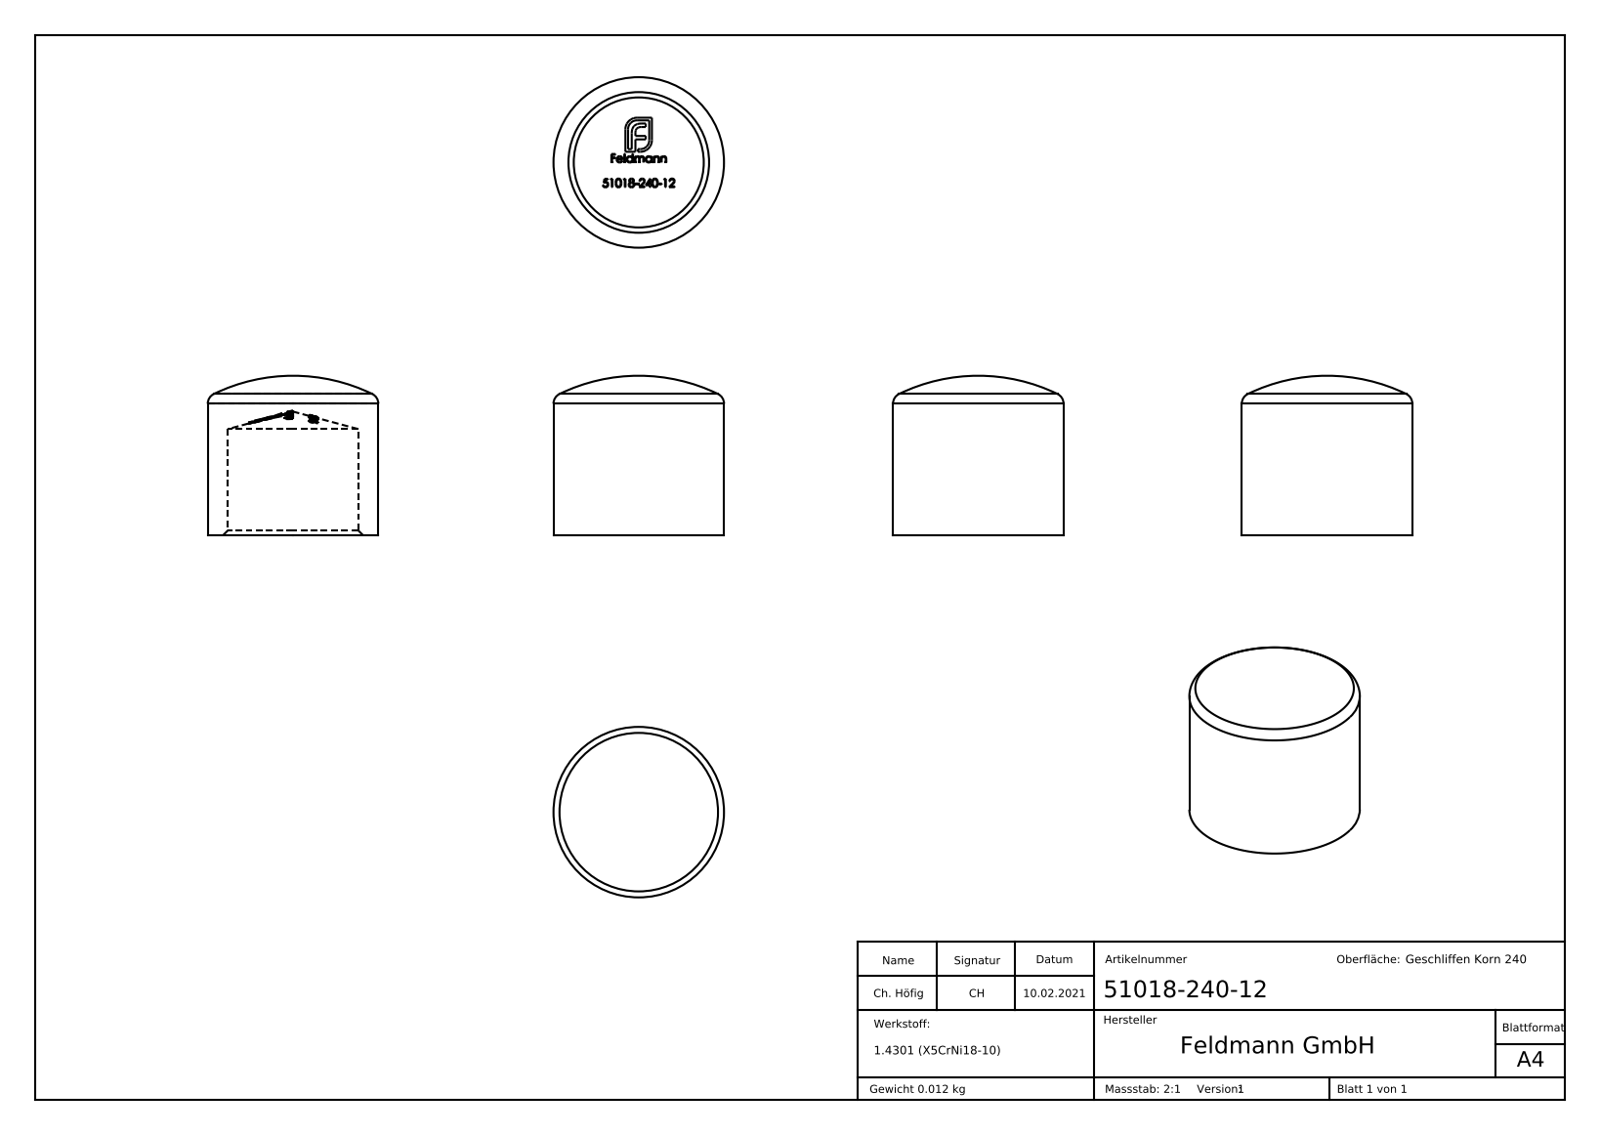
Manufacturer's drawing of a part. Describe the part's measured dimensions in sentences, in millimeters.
The part is named "51018-240-12". Its 3-D file was written by "SolidWorks 2018 (CONFIG_CONTROL_DESIGN)". It is 1 solid with 303 faces: 132 planar, 4 cylindrical and 167 other. Overall it measures 16 by 16 by 15 millimeters. Its volume is 1 578 cubic millimeters and its surface area 1 447 square millimeters. Round holes: 1 of diameter 12.2. Round bosses or shafts: 1 of diameter 16. The main face-to-face distances are 2.23, 1.89, 1.98, 1.21, 3.32, 1.29, 0.71, 2.48, 0.34, 1.49.
